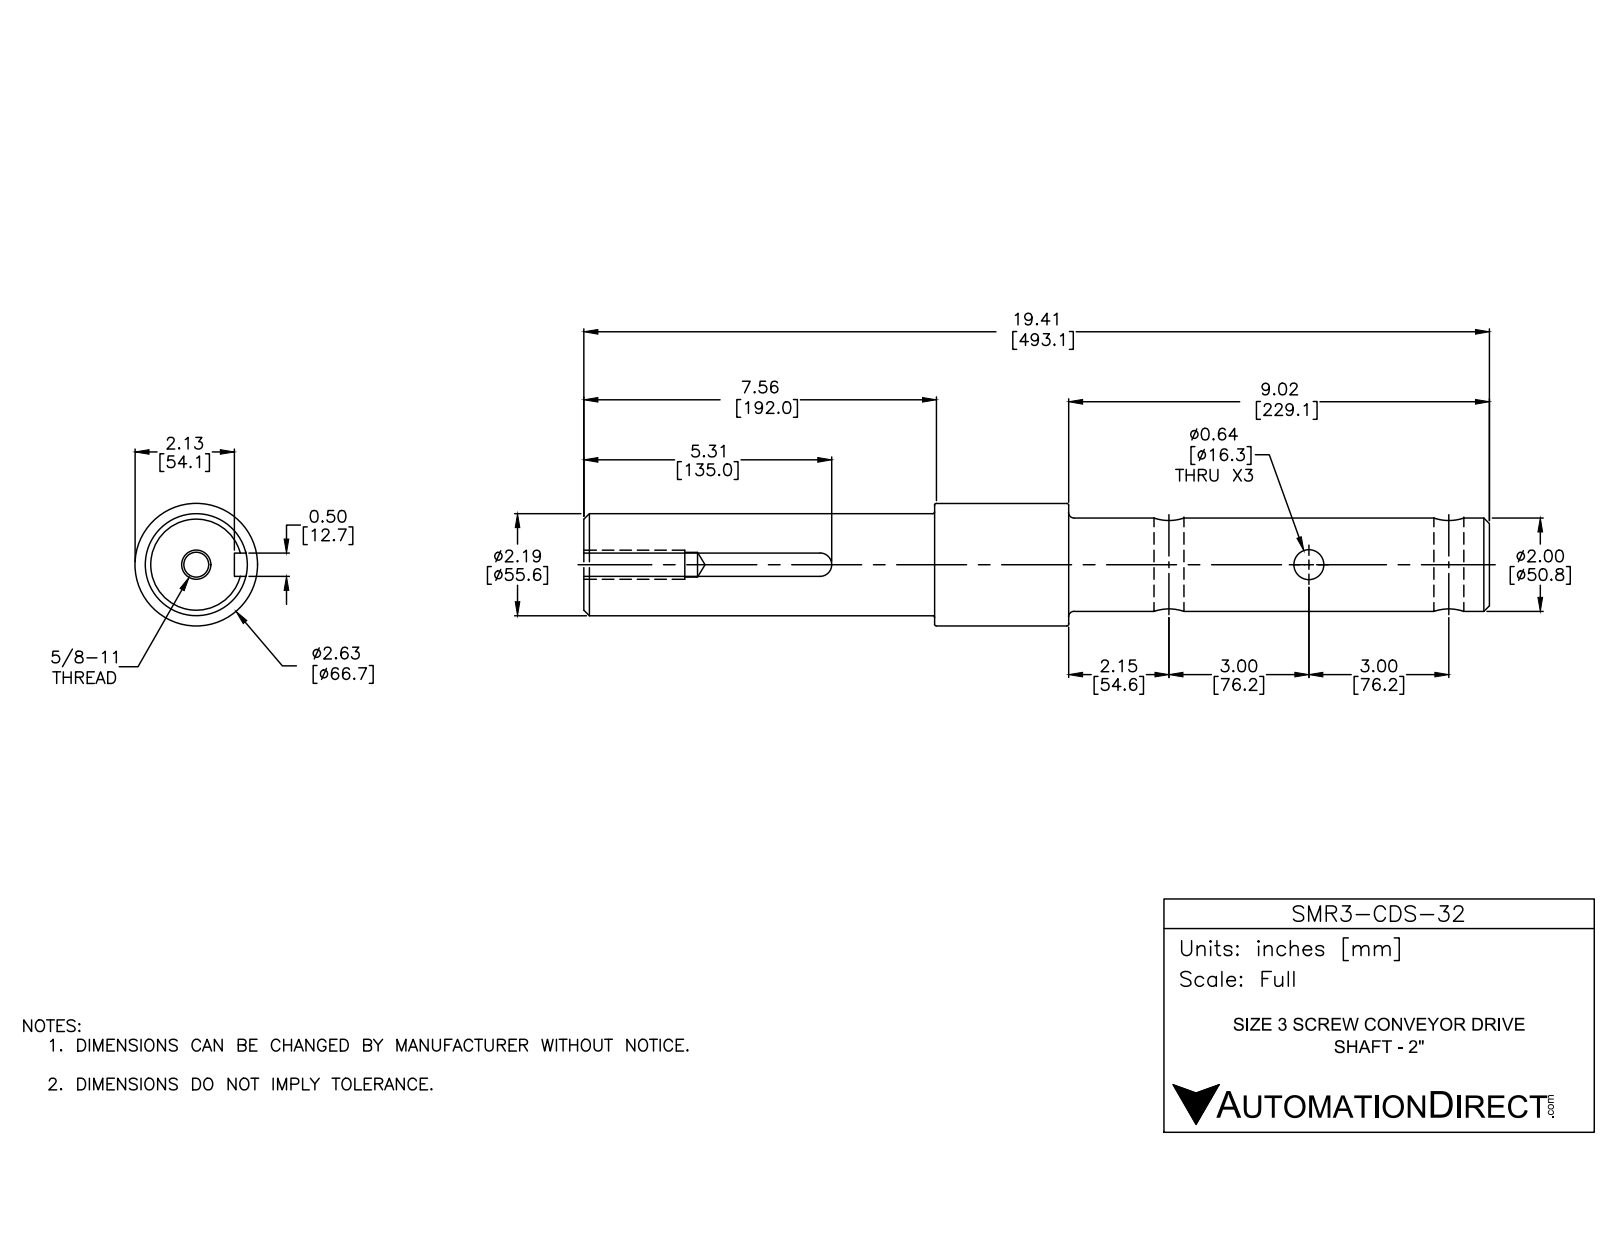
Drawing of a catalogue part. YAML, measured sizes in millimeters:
part_name: "SMR3-CDS-32"
step_written_by: "SolidWorks 2016 (AUTOMOTIVE_DESIGN)"
units: millimeters
bodies: {solids: 1, faces: 40, planar: 8, cylindrical: 18, other: 14}
overall_size: [493.1, 66.7, 66.7]
volume: 1126000
surface_area: 102200
round_holes:
  - {diameter: 16.3, count: 3}
  - {diameter: 13.5, count: 1}
  - {diameter: 15.9, count: 1}
round_bosses_or_shafts:
  - {diameter: 66.7, count: 1}
  - {diameter: 55.5, count: 1}
  - {diameter: 50.8, count: 1}
partial_cylinders:
  - {radius: 6.4, count: 1}
face_to_face_distances: [493.1, 12.7, 264, 229.1, 191, 73, 302.1, 55, 136, 209]
hole_center_spacings: [152.4]
